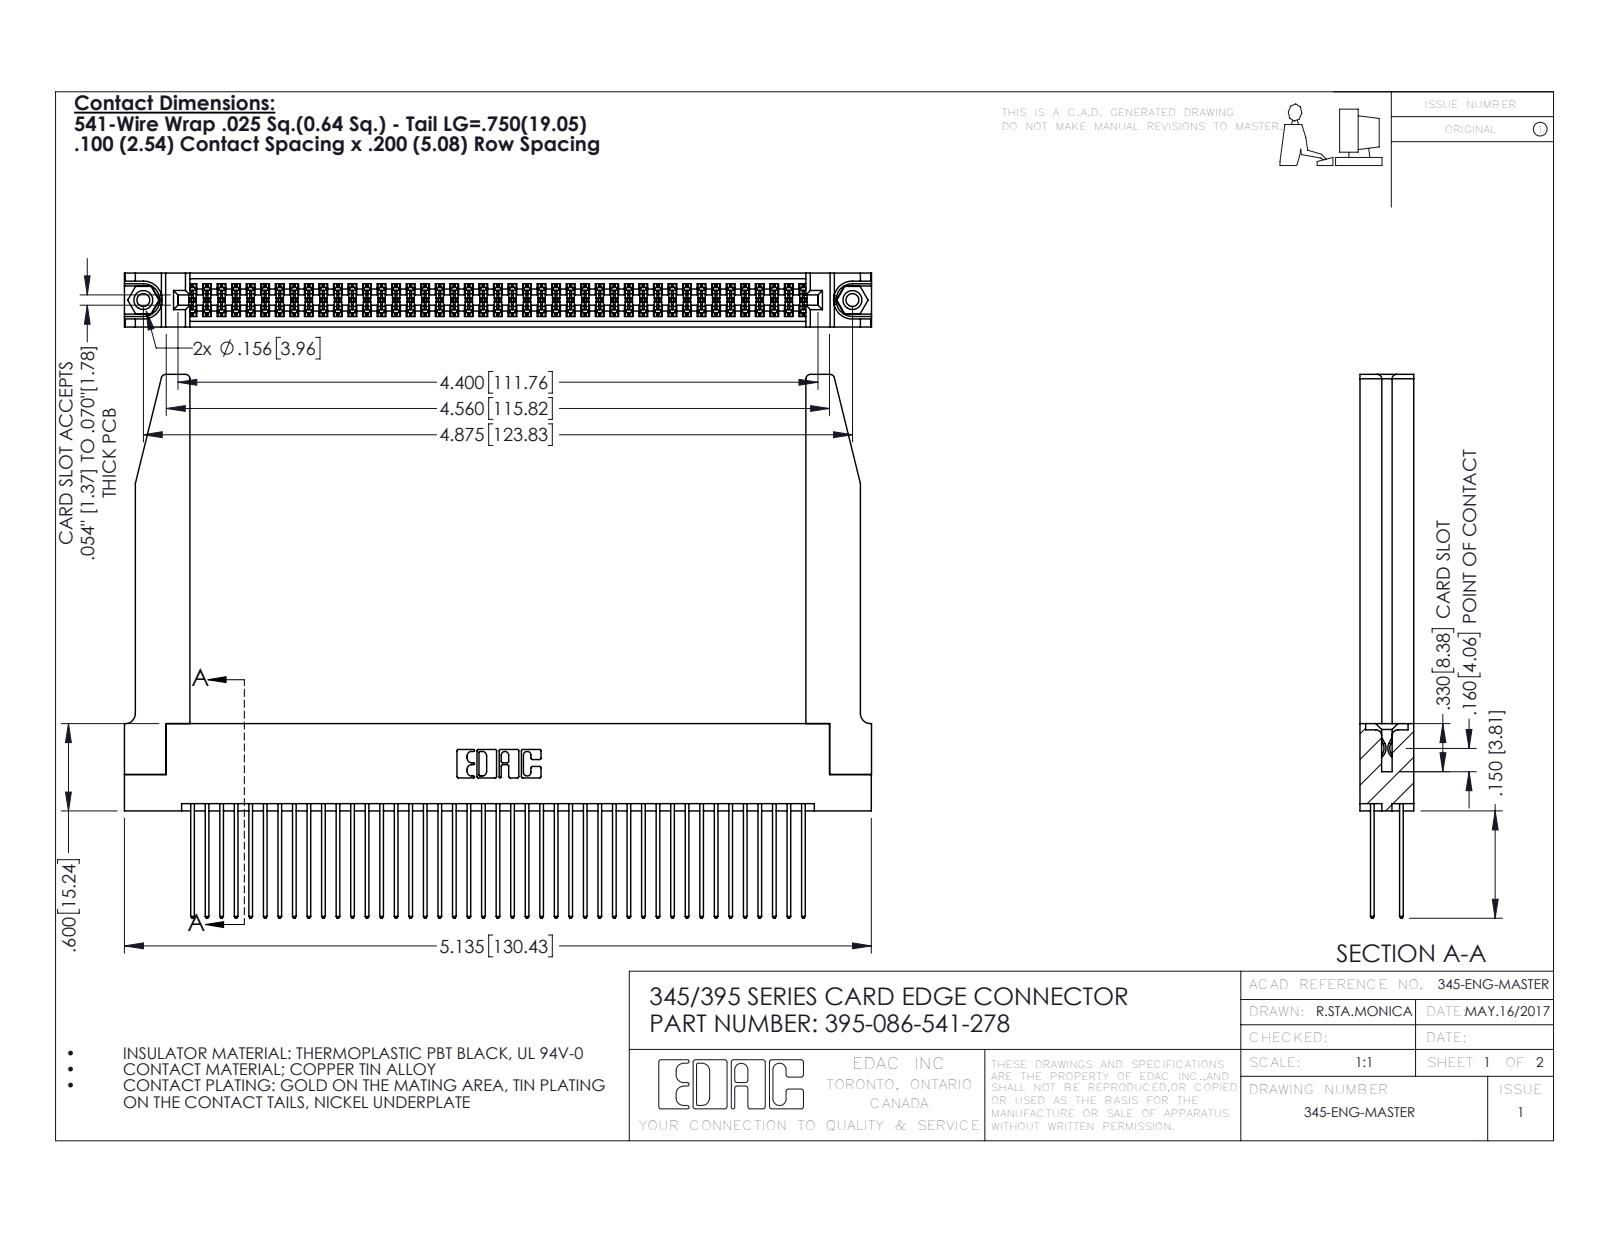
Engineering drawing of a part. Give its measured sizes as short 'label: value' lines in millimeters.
name: 395-086-541-278; 345 Part_Flush Mounting Lugs - 0.156 Dia-TH; 345-220-078_345-220-078; 345-250-001_345-250-001-102 (+1 more)
written by: SolidWorks 2016 (CONFIG_CONTROL_DESIGN)
unit: mm
bodies: 91 solids, 4660 faces (3060 planar, 1548 cylindrical, 52 other)
size: 130.5 × 94.9 × 9.4
volume: 20 940 mm³; area: 28 650 mm²
holes: 2× ⌀2.3, 2× ⌀3.2, 2× ⌀4, 1× ⌀1.6
bosses: 2× ⌀3.9
rounds: 129× R0.2, 86× R0.3, 22× R0.3, 8× R0.8, 6× R0.2, 6× R0.8, 3× R0.7, 2× R0.4
face distances: 1.8, 7.6, 9.4, 5.1, 2.5, 6.9, 0.6, 5.7, 4.4, 3.8
hole spacings: 6.9, 117.8, 123.8
